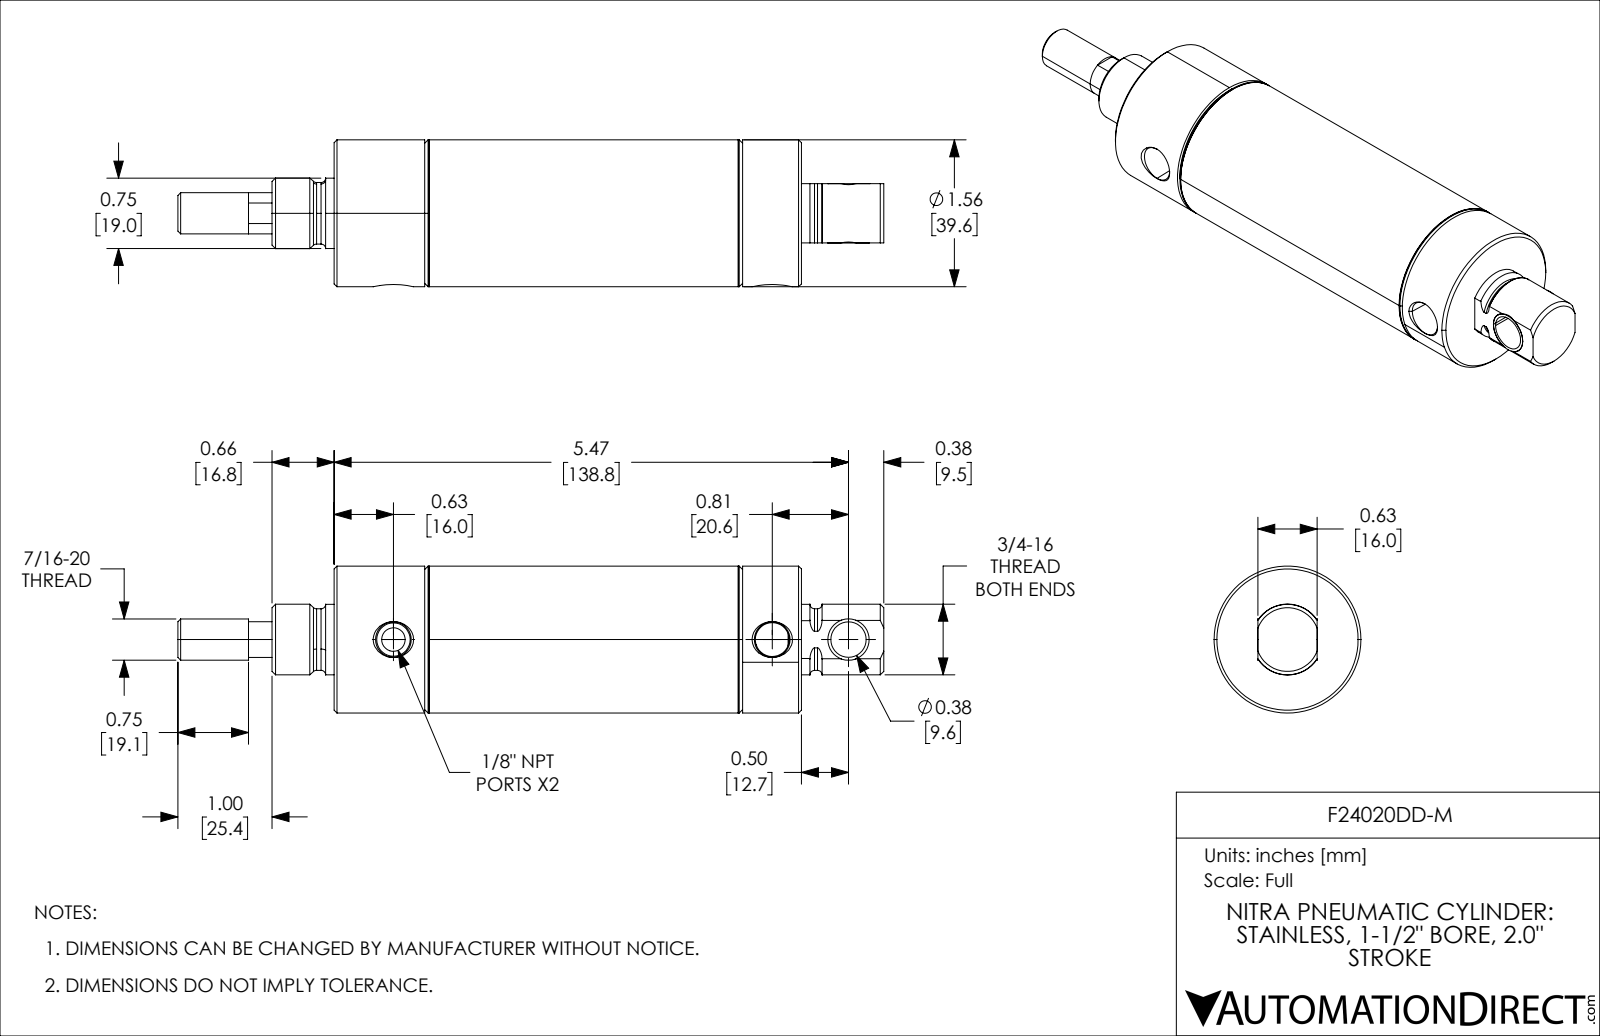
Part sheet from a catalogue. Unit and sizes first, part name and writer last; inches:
Units: inches
Overall size (bounding box): 7.5 × 1.56 × 1.56
Round holes (diameter × count): ⌀0.25 ×1, ⌀0.36 ×1, ⌀0.376 ×1, ⌀0.439 ×1, ⌀0.462 ×1, ⌀0.532 ×1, ⌀1.062 ×1, ⌀1.431 ×1
Round bosses / shafts (diameter × count): ⌀1.56 ×1, ⌀1.511 ×1, ⌀0.75 ×1, ⌀0.748 ×1, ⌀0.654 ×1, ⌀0.654 ×1, ⌀0.438 ×1, ⌀0.437 ×1
Main face-to-face distances: 0.875, 1.75, 2, 2.875, 3.75, 0.875, 1.215, 3.215, 4.09, 4.965
Hole centre spacings: 0.81, 4.025, 4.835
Volume: 6.37 in³ · Surface area: 77.25 in²
Bodies: 5 solids, 157 faces (35 planar, 58 cylindrical, 64 other)
Part name (STEP PRODUCT): F24020DD-M_3; F24020DD-M_7; F24020DD-M_5; F24020DD-M_11 (+2 more)
STEP written by: SolidWorks 2021 (CONFIG_CONTROL_DESIGN)
